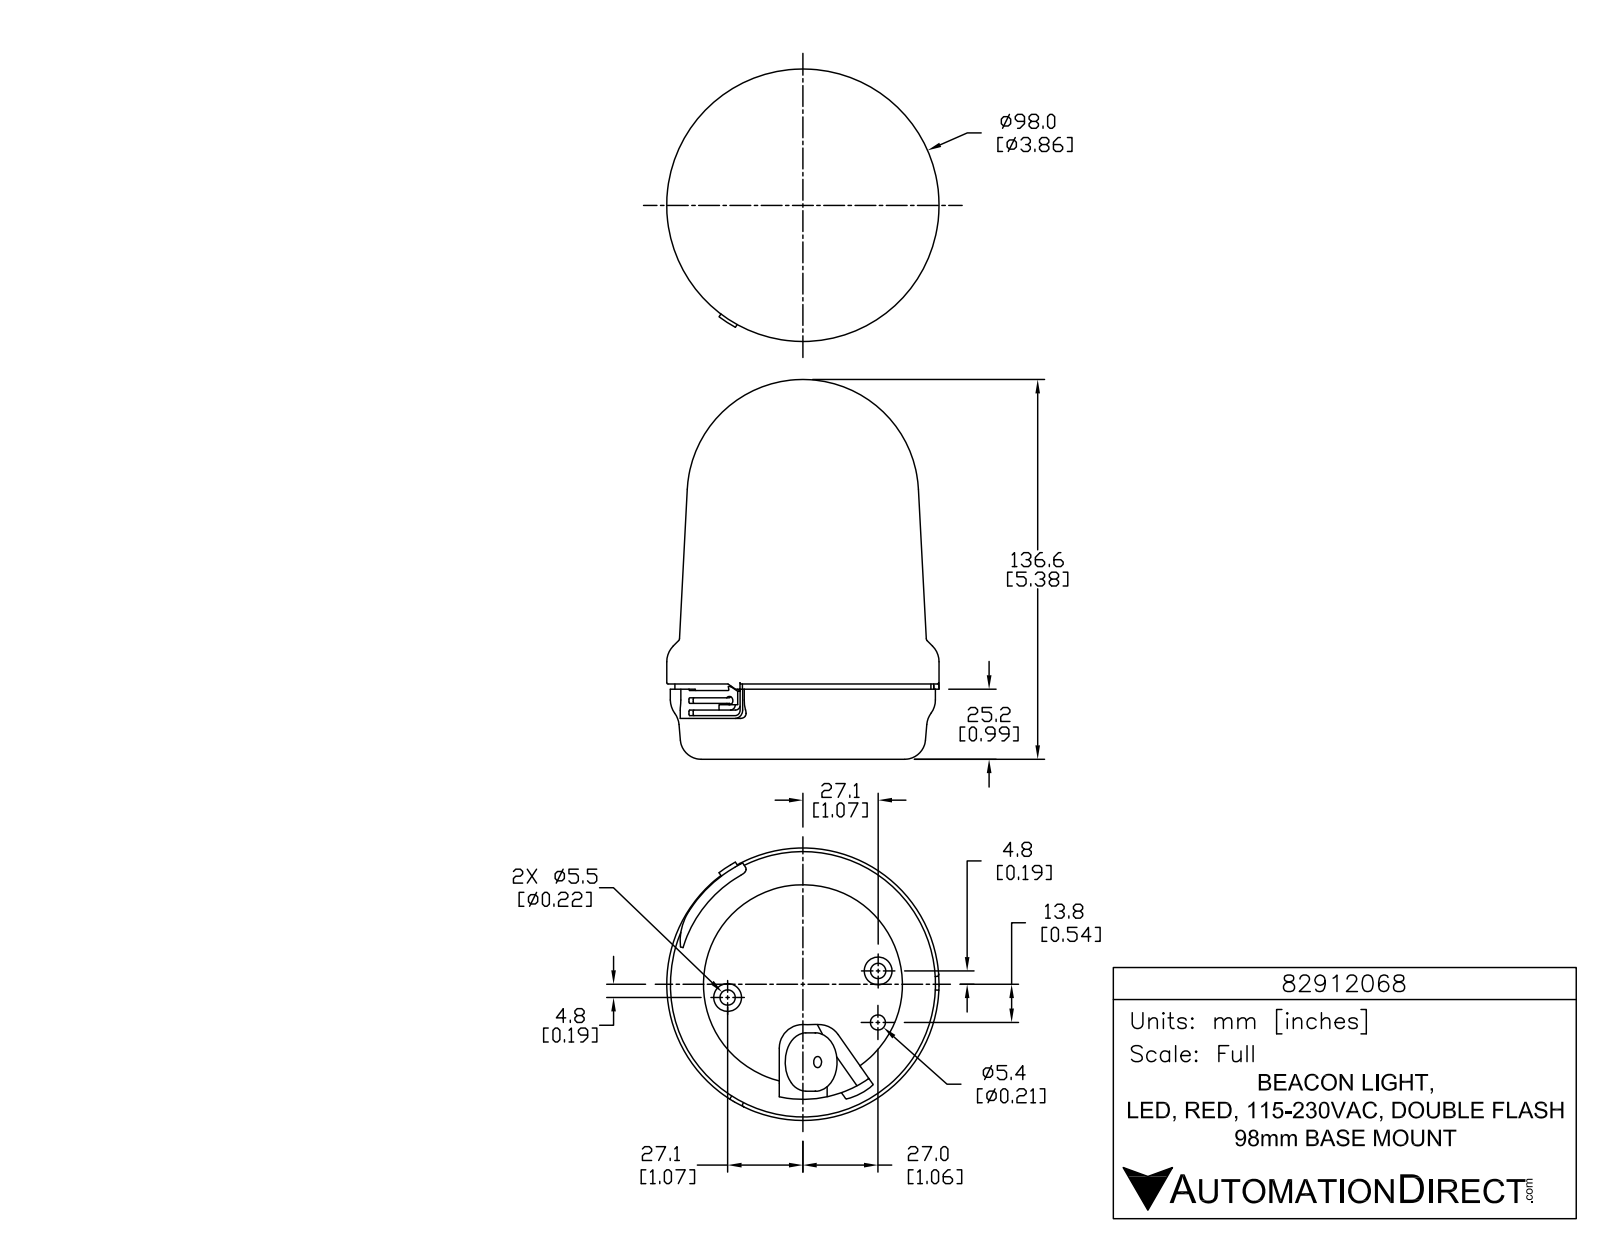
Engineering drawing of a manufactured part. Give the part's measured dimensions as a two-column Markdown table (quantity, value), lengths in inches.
| quantity | value |
| --- | --- |
| part name | 82912068 |
| STEP written by | SolidWorks 2015 (AUTOMOTIVE_DESIGN) |
| units | inches |
| bodies | 1 solid, 872 faces (566 planar, 204 cylindrical, 102 other) |
| overall size | 5.378 × 3.858 × 3.858 |
| volume | 44.69 in³ |
| surface area | 73.66 in² |
| round holes (diameter × count) | 0.059 × 3, 0.217 × 2, 0.157 × 1, 0.213 × 1, 2.819 × 1 |
| round bosses / shafts (diameter × count) | 0.339 × 3, 0.084 × 3, 0.394 × 2, 3.858 × 1, 3.756 × 1, 3.626 × 1, 0.827 × 1 |
| partial cylindrical surfaces (radius × count) | 0.005 × 9, 0.005 × 6, 0.012 × 6, 0.012 × 6, 0.012 × 6, 0.196 × 6, 0.02 × 5, 0.039 × 4 |
| main face-to-face distances | 1.045, 0.972, 0.073, 0.02, 0.992, 1.065, 0.236, 0.579, 0.559, 0.413 |
| hole center spacings | 1.083, 0.73, 1.193, 2.158, 2.165 |
